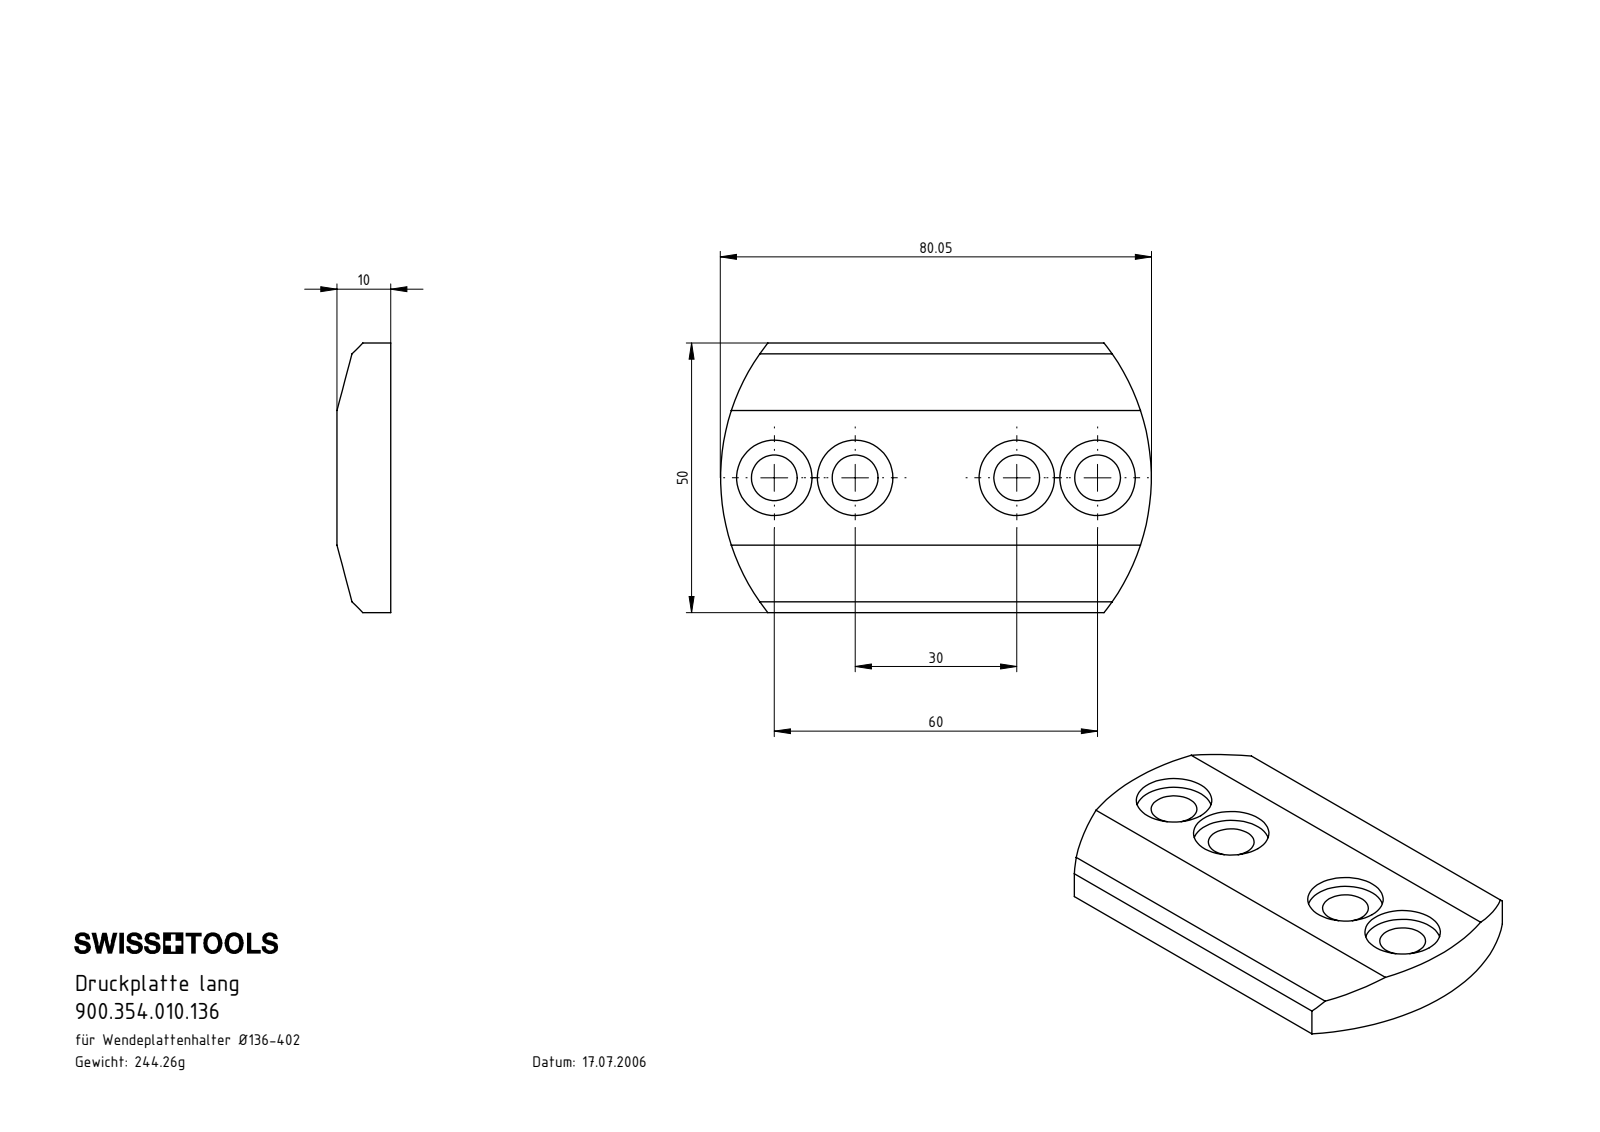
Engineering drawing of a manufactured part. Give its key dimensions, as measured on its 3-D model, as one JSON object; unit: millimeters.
{"part_name": "900.354.010.136", "step_written_by": "SolidWorks 2022 (AUTOMOTIVE_DESIGN)", "units": "millimeters", "bodies": {"solids": 1, "faces": 30, "planar": 12, "cylindrical": 18, "other": 0}, "overall_size": [79.95, 50, 10], "volume_mm3": 31116, "surface_area_mm2": 9971, "round_holes": [[8.5, 4], [14, 4]], "partial_cylinders_radius": [[40, 2]], "face_to_face_distances": [10, 8, 2, 50], "hole_center_spacings": [15, 45, 30, 60]}
